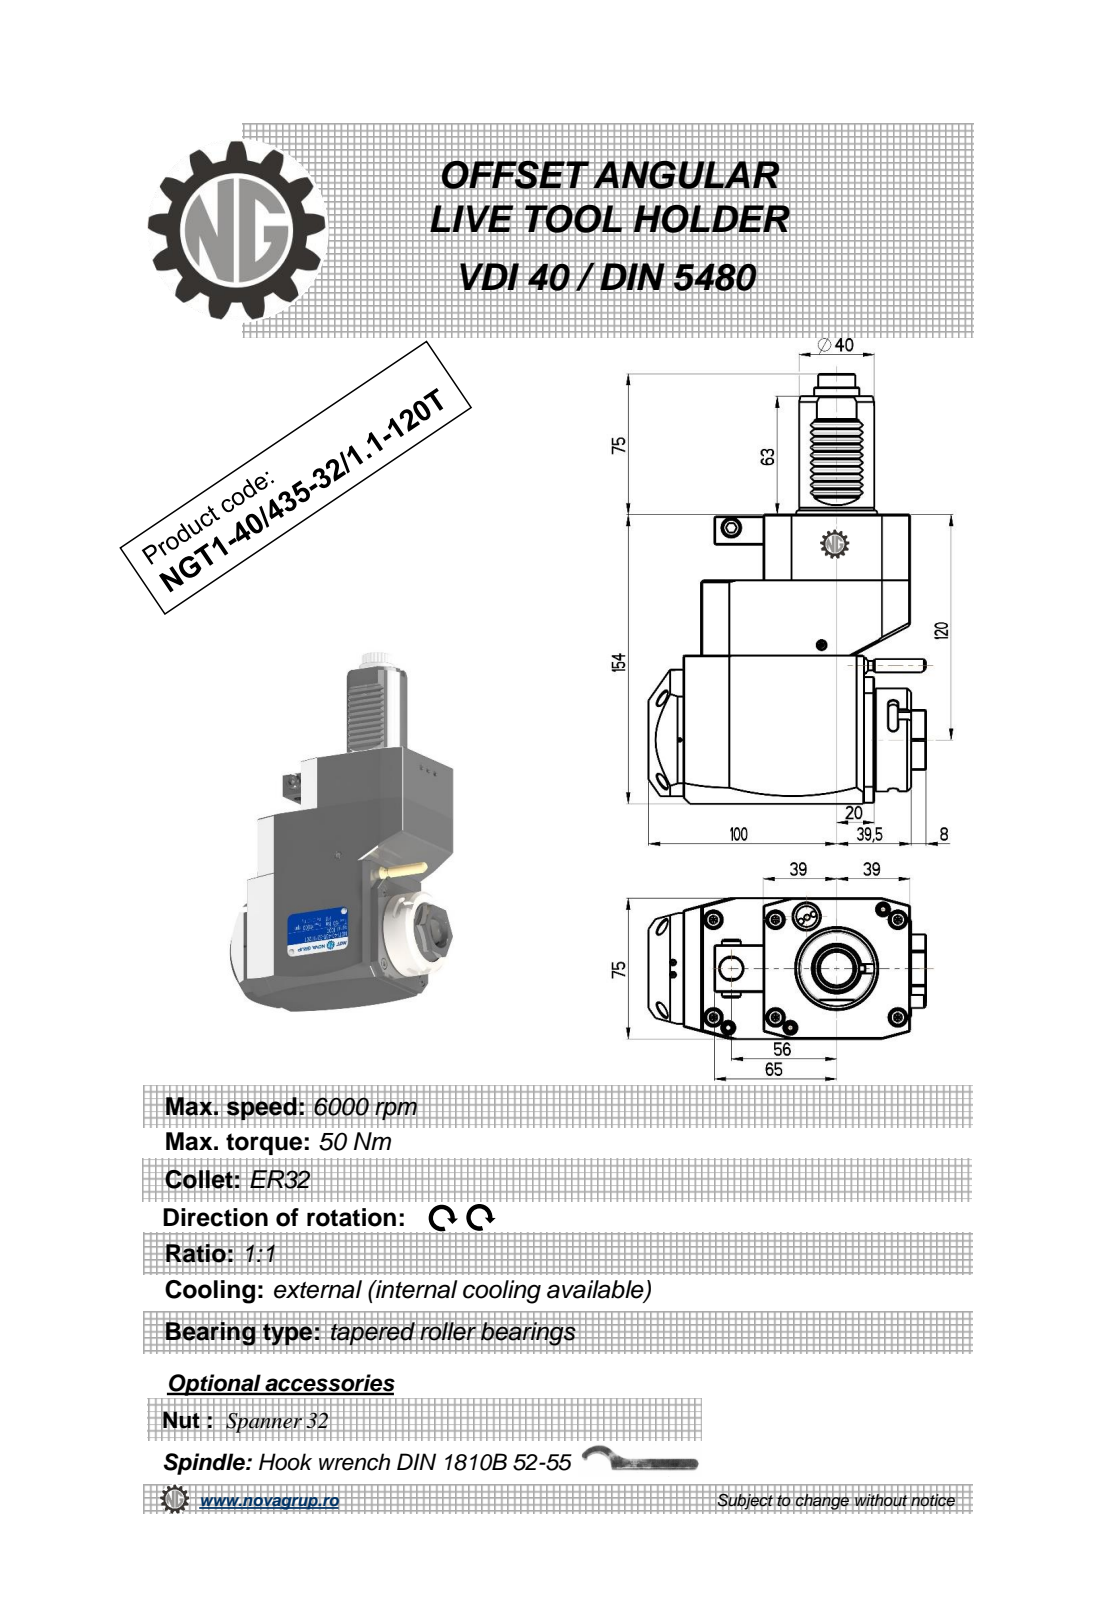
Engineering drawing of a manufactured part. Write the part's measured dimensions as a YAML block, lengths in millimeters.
part_name: "NGT1_40_435_32_1_1_120T"
step_written_by: "PRO/ENGINEER BY PARAMETRIC TECHNOLOGY CORPORATION, 2010280 (CONFIG_CONTROL_DESIGN)"
units: millimeters
bodies: {solids: 1, faces: 449, planar: 195, cylindrical: 160, other: 94}
overall_size: [229, 147.5, 75]
volume: 1276000
surface_area: 89493
round_holes:
  - {diameter: 2.5, count: 1}
  - {diameter: 3, count: 1}
  - {diameter: 8.5, count: 1}
  - {diameter: 9.5, count: 1}
  - {diameter: 12, count: 1}
  - {diameter: 23, count: 1}
round_bosses_or_shafts:
  - {diameter: 8.96, count: 2}
  - {diameter: 55, count: 1}
  - {diameter: 48, count: 1}
  - {diameter: 40, count: 1}
  - {diameter: 24, count: 1}
  - {diameter: 10, count: 1}
  - {diameter: 7, count: 1}
  - {diameter: 5, count: 1}
partial_cylinders:
  - {radius: 2.08, count: 48}
  - {radius: 0.3, count: 10}
  - {radius: 2.5, count: 6}
  - {radius: 180, count: 2}
  - {radius: 9.08, count: 1}
  - {radius: 9.92, count: 1}
  - {radius: 15, count: 1}
  - {radius: 24.5, count: 1}
face_to_face_distances: [75, 154, 19, 35, 111, 59, 92, 119, 0.5, 33]
hole_center_spacings: [43.2, 74.1, 111.5]
